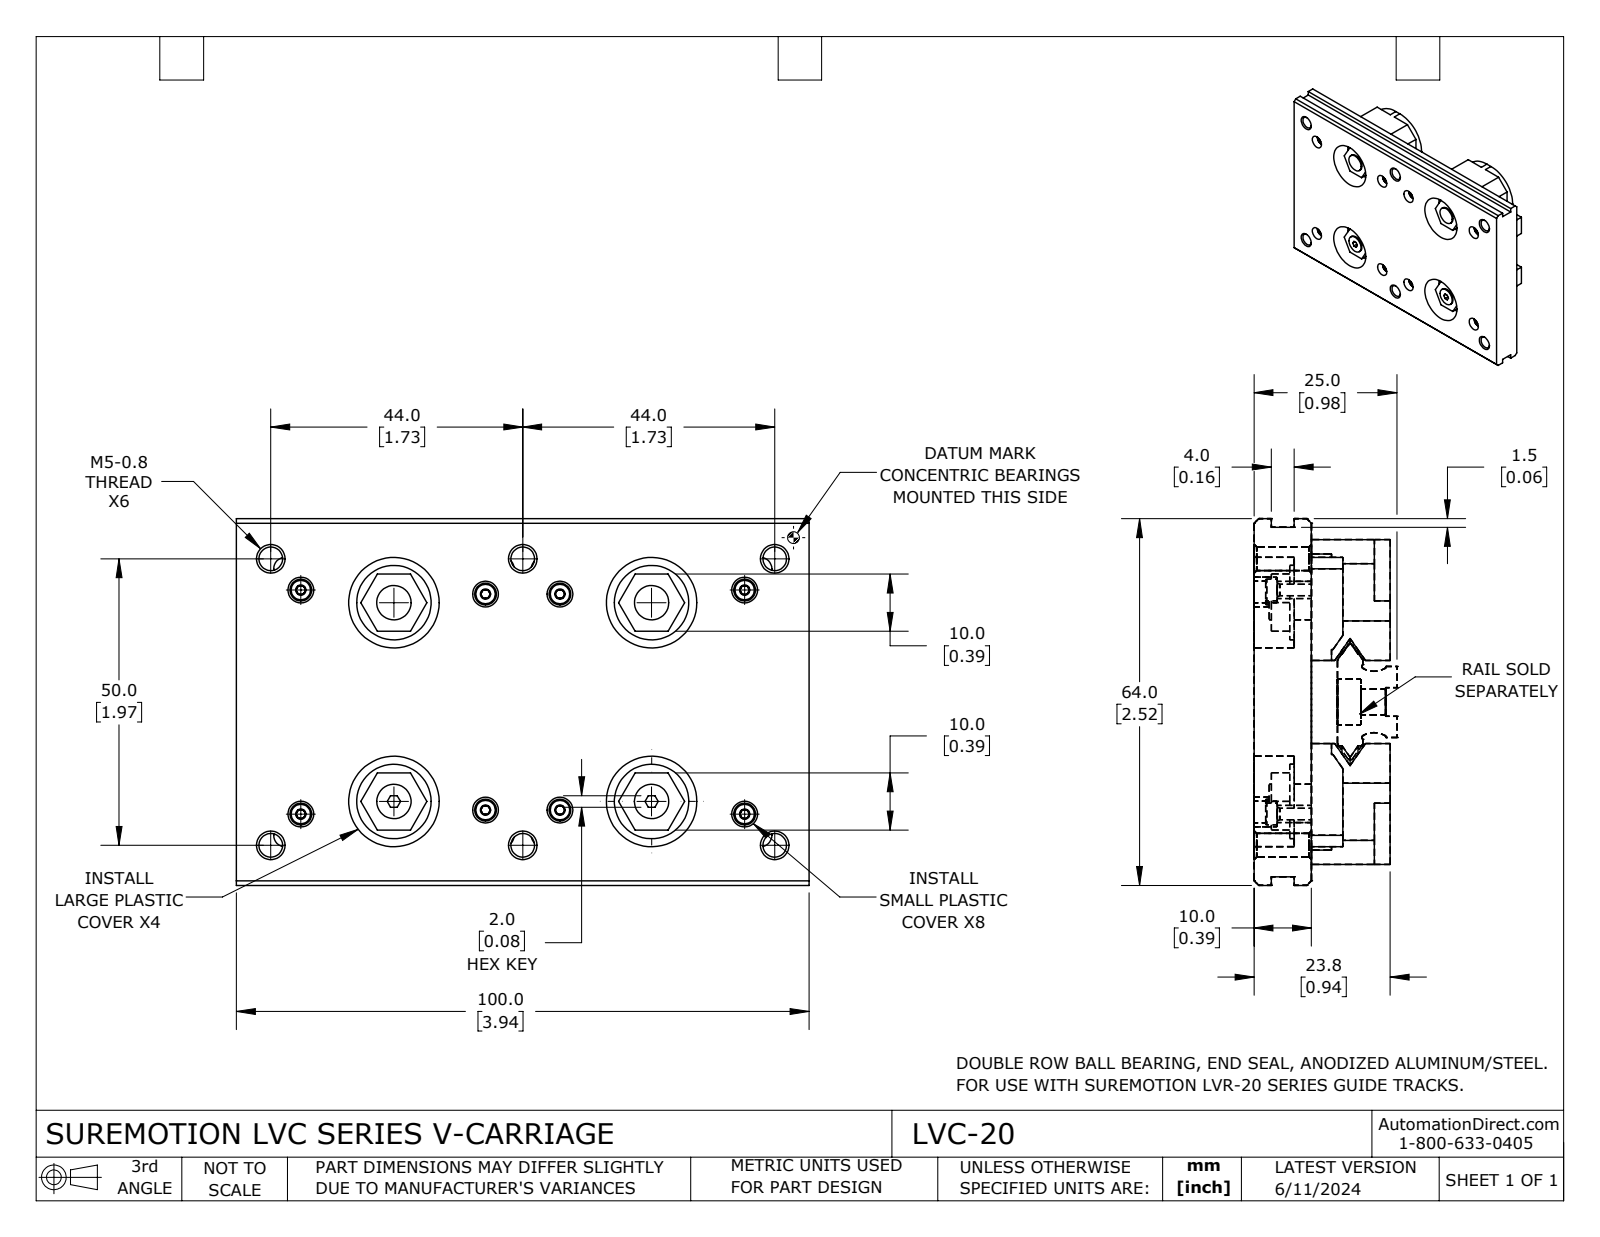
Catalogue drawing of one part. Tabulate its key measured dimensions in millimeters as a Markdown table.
| quantity | value |
| --- | --- |
| part name | LVC-20 |
| STEP written by | SolidWorks 2023 (CONFIG_CONTROL_DESIGN) |
| units | millimeters |
| bodies | 17 solids, 760 faces (396 planar, 180 cylindrical, 184 other) |
| overall size | 100 × 64 × 23.75 |
| volume | 101 270 mm³ |
| surface area | 39 805 mm² |
| round holes (diameter × count) | 1.57 × 8, 3 × 8, 4.5 × 8, 4.13 × 6, 15.8 × 4 |
| round bosses / shafts (diameter × count) | 3.8 × 8, 2 × 8, 18 × 4, 13 × 4, 7 × 4, 6 × 4 |
| partial cylindrical surfaces (radius × count) | 2 × 16, 10.7 × 8 |
| main face-to-face distances | 10, 3, 13.75, 23.75, 7, 11.75, 16.75, 2, 5.5, 8.25 |
| hole center spacings | 16.4, 40.32, 45, 0.74, 7.57, 8.29, 8.95, 12.77 |
